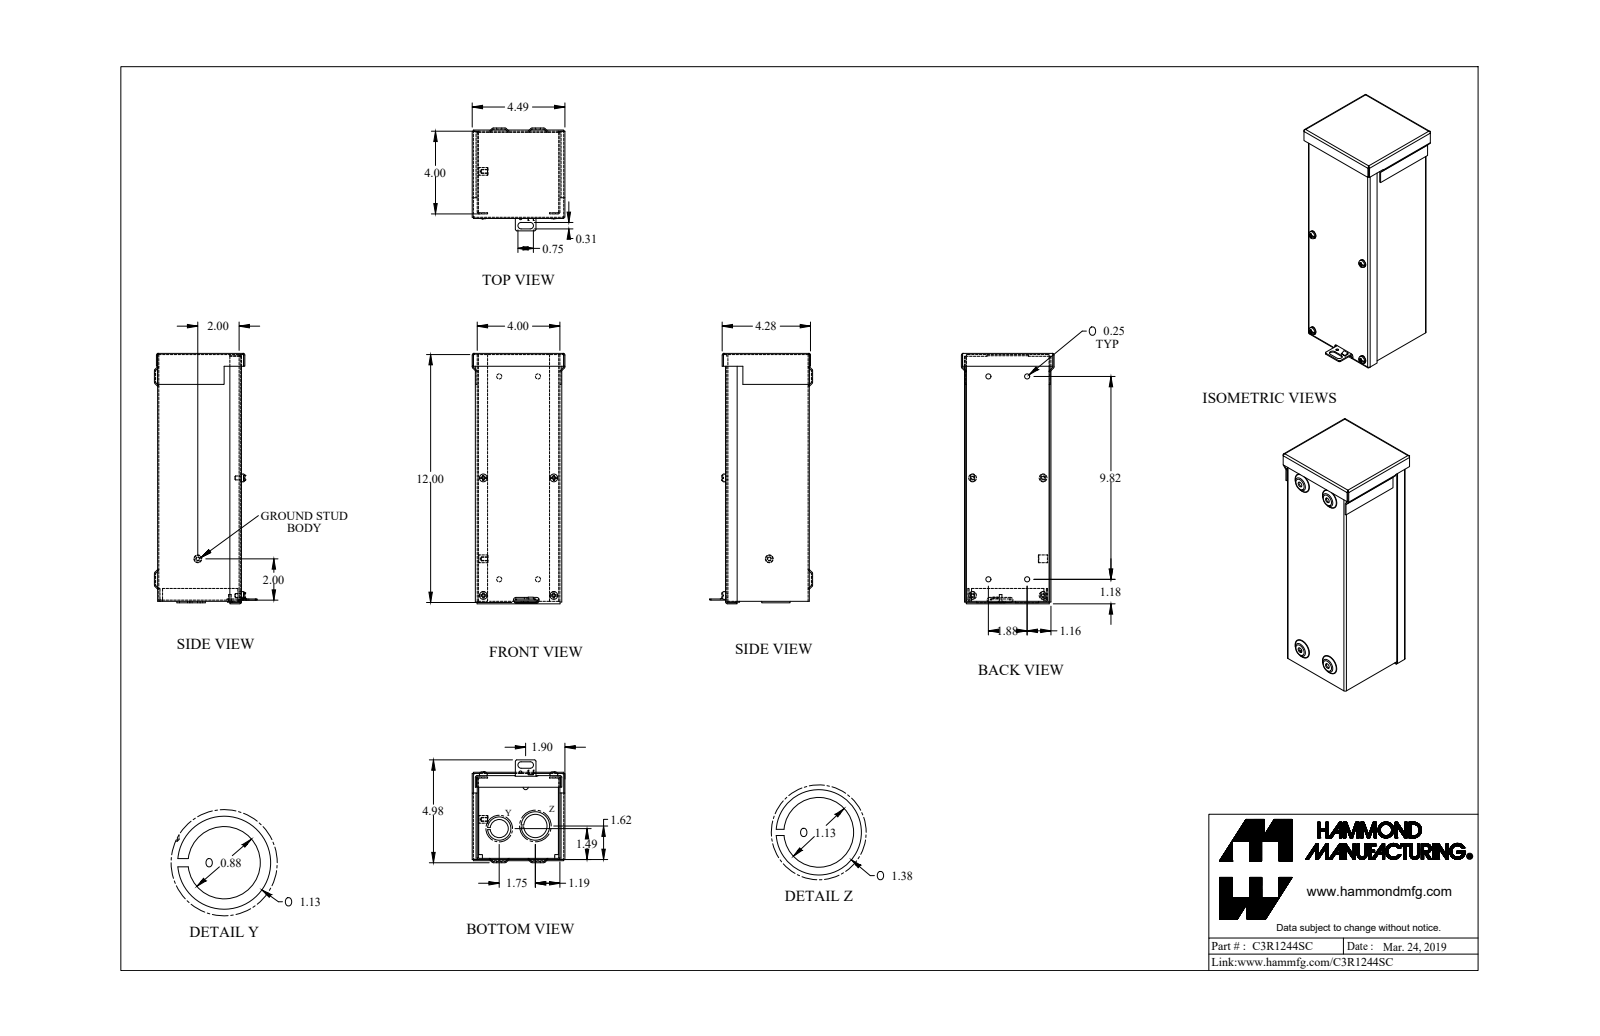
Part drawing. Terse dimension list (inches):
name: C3R1244SC_Default
written by: SolidWorks 2019 (CONFIG_CONTROL_DESIGN)
unit: in
bodies: 11 solids, 414 faces (217 planar, 111 cylindrical, 86 other)
size: 12.12 × 4.977 × 4.489
volume: 15.77 in³; area: 559.5 in²
holes: 4× ⌀0.17, 4× ⌀0.25, 1× ⌀0.125, 1× ⌀0.137, 1× ⌀0.156, 1× ⌀0.875, 1× ⌀1.125
bosses: 4× ⌀0.19, 3× ⌀0.375, 2× ⌀0.375, 1× ⌀1.375, 1× ⌀1.125, 1× ⌀0.125
rounds: 21× R0.029, 21× R0.086, 8× R0.109, 8× R0.125, 2× R0.156
face distances: 0.057, 3.943, 4, 3.886, 4.057, 0.057, 0.114, 11.886, 11.943, 11.943
hole spacings: 4.969, 5.576, 1.096, 1.875, 2.757, 3.414, 5.69, 6.636
